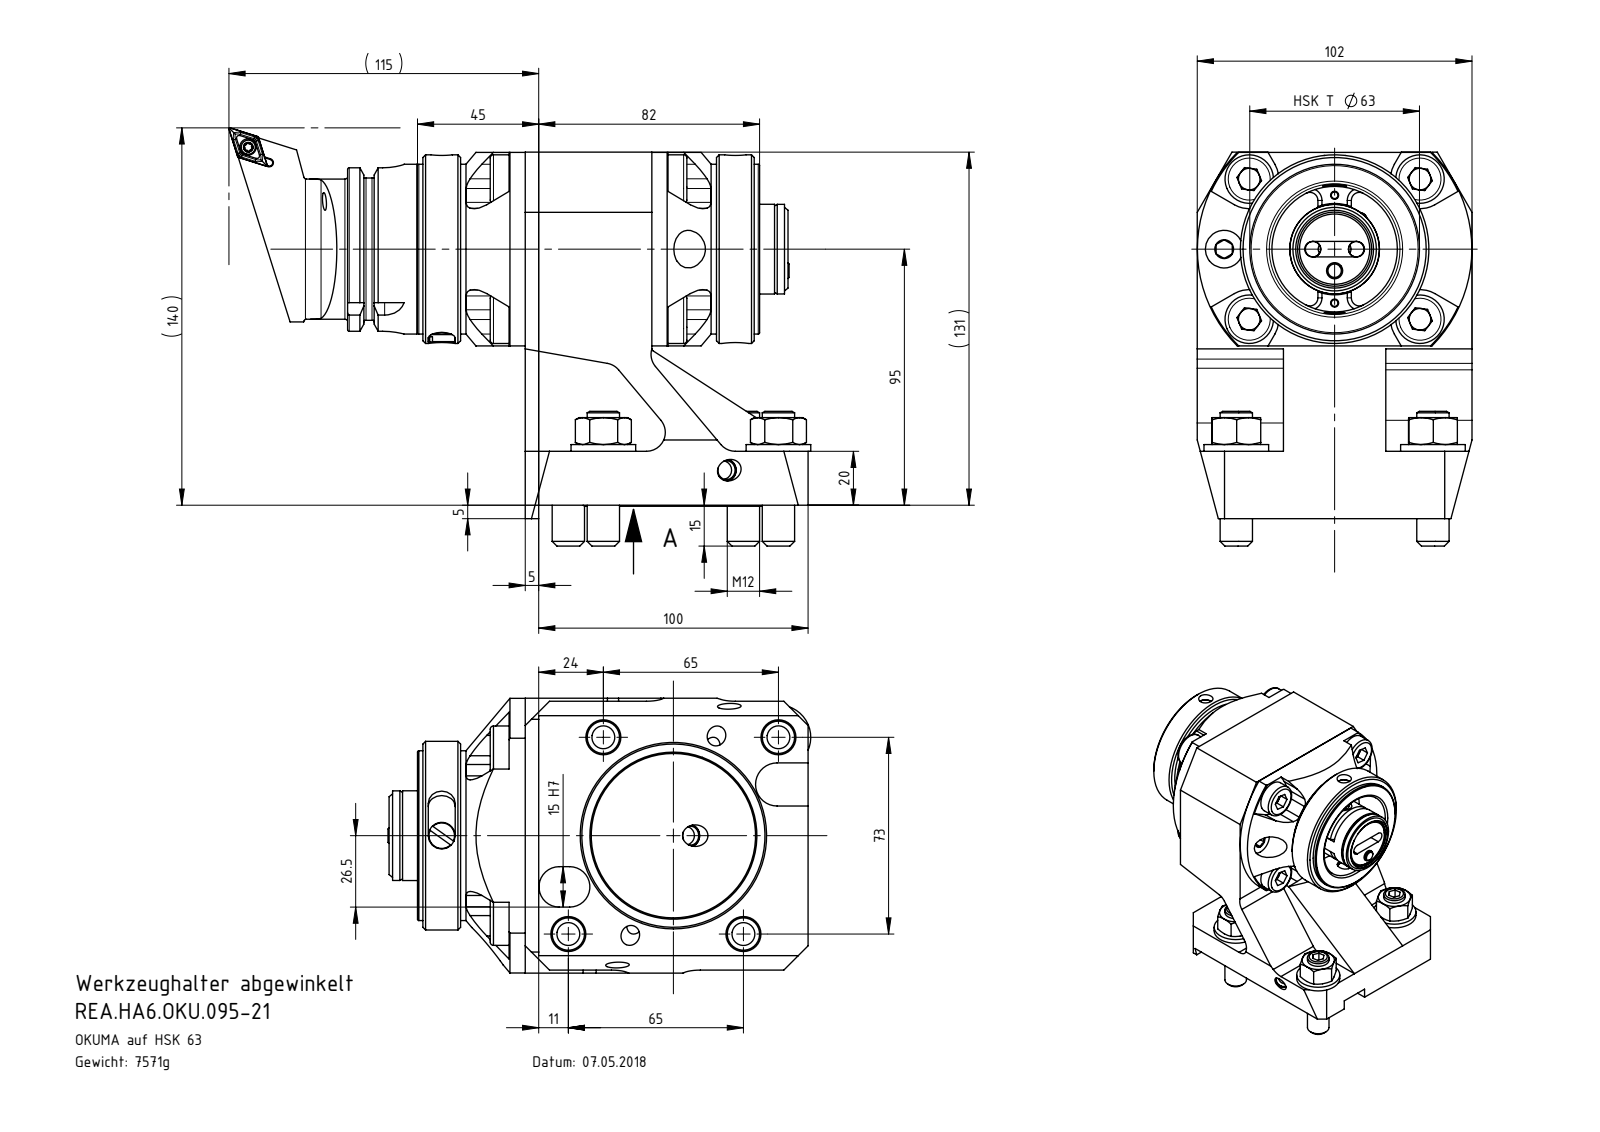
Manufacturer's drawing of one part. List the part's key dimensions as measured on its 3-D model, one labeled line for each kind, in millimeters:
Part name (STEP PRODUCT): DIN 7984 - M12 x 20_DIN 7984 - M12 x 20 --- 20N; ISO 13337 - 5 x 14_ISO13337 5x16; HA6-ER1.001.000; DIN 3771 - 58x2.5 (+8 more)
STEP written by: SolidWorks 2017 (AUTOMOTIVE_DESIGN)
Units: millimetres
Bodies: 54 solids, 1049 faces (500 planar, 285 cylindrical, 264 other)
Overall size (bounding box): 156.95 × 146.17 × 102
Volume: 968 597 mm³ · Surface area: 245 107 mm²
Round holes (diameter × count): ⌀10.2 ×8, ⌀13 ×8, ⌀6.8 ×6, ⌀8 ×5, ⌀5.8 ×4, ⌀12 ×4, ⌀7 ×3, ⌀2.5 ×2, ⌀4 ×2, ⌀5 ×2, ⌀5.75 ×2, ⌀8.5 ×2
Round bosses / shafts (diameter × count): ⌀24 ×4, ⌀18 ×4, ⌀12 ×4, ⌀8 ×3, ⌀16 ×2, ⌀13 ×2, ⌀9.9 ×2, ⌀5.9 ×2
Partial cylindrical surfaces — rounded edges, fillets, slot ends (radius × count): R3 ×14, R5 ×8, R7 ×8, R11 ×5, R1 ×4, R2.9 ×4, R8 ×3, R2.88 ×2
Main face-to-face distances: 20, 27, 32, 47, 40, 111, 33, 70, 7, 31.9
Hole centre spacings: 41, 21.54, 27.61, 32.26, 35.18, 45.62, 47.46, 55.86
